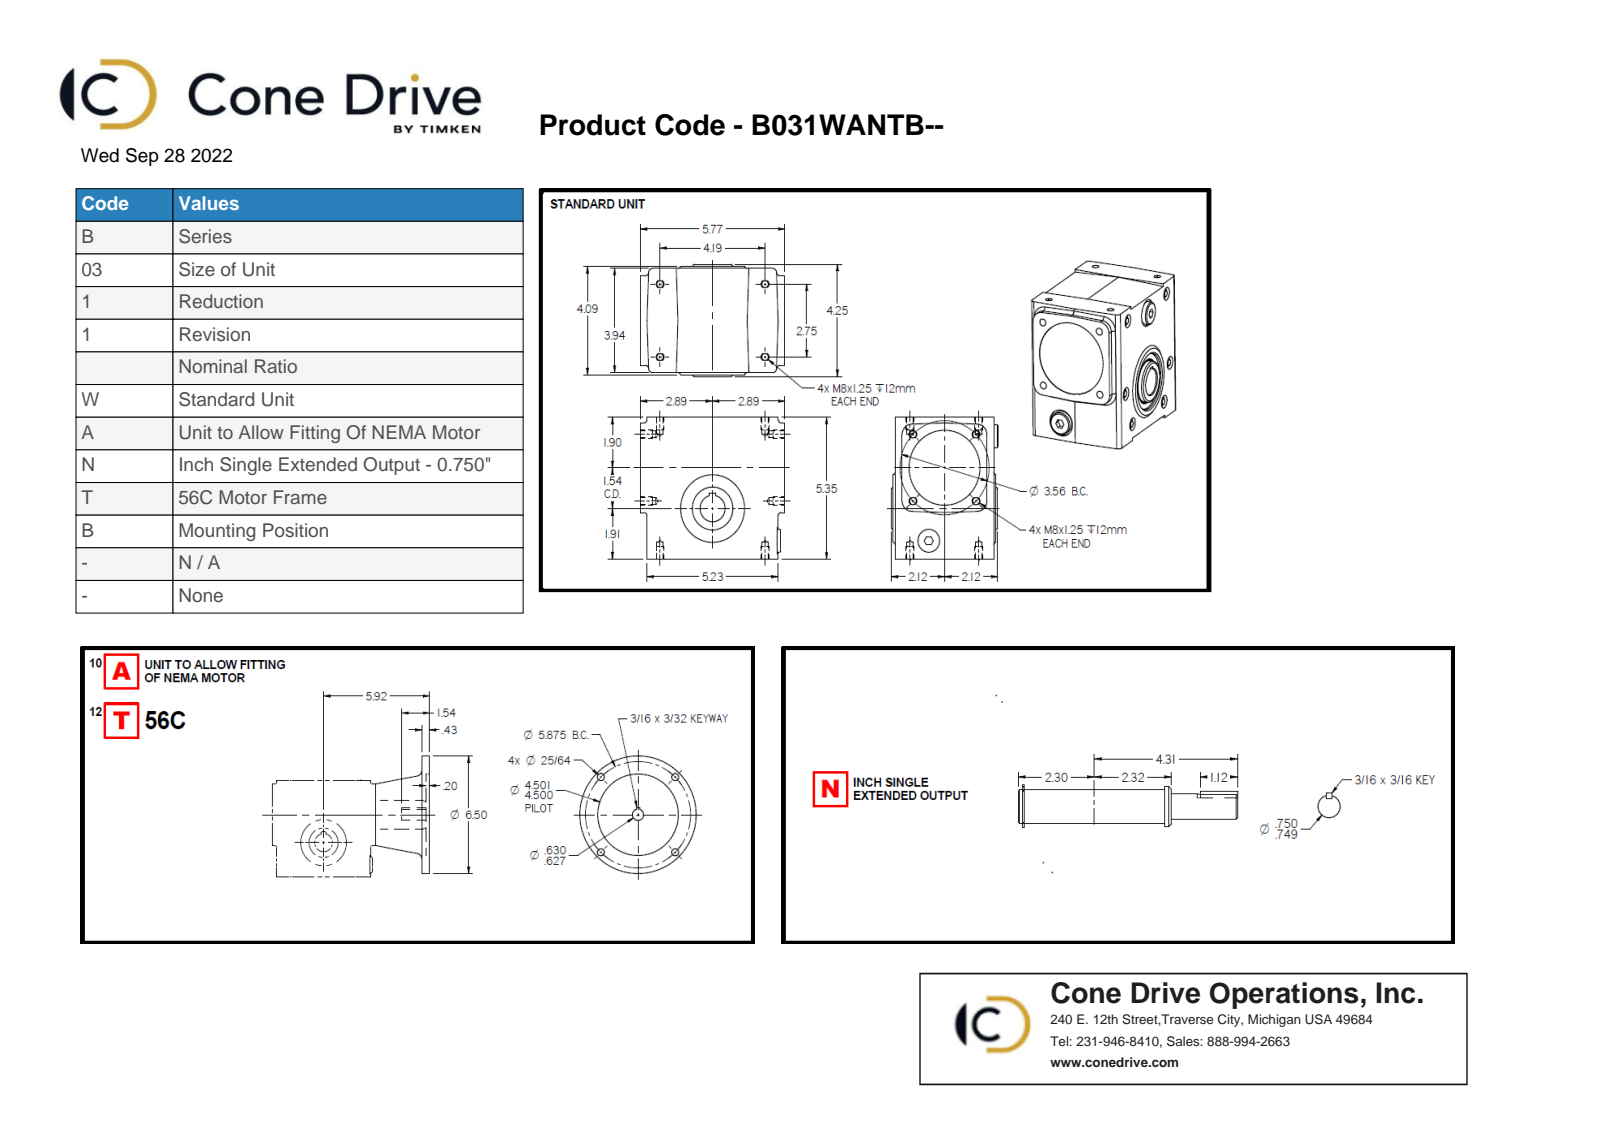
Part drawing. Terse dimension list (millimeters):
name: B031110.WANTB; B03-1-CP; B03-0N-CP; B03-04T-CP
written by: Solid Edge (AUTOMOTIVE_DESIGN)
unit: mm
bodies: 13 solids, 576 faces (300 planar, 148 cylindrical, 128 other)
size: 223.61 × 192.02 × 170.69
volume: 2 005 000 mm³; area: 315 366 mm²
holes: 6× ⌀12.5, 4× ⌀6.65, 4× ⌀6.92, 4× ⌀8.8, 4× ⌀10, 2× ⌀1.98, 2× ⌀26, 1× ⌀12.7, 1× ⌀15.94, 1× ⌀19, 1× ⌀25.4, 1× ⌀25.41
bosses: 6× ⌀10, 6× ⌀6, 4× ⌀12.85, 3× ⌀0.51, 2× ⌀39.92, 2× ⌀22, 1× ⌀165.1, 1× ⌀71.21
rounds: 12× R3.17, 4× R0.25, 4× R3.99, 4× R7.5, 4× R10, 2× R0.2, 2× R0.61, 2× R2.54
face distances: 99.95, 77, 66.2, 10.8, 17, 129.6, 135.85, 14.5, 2.5, 144.1
hole spacings: 87.27, 29.36, 45.25, 64, 74.61, 105.52, 119.87, 14.51
